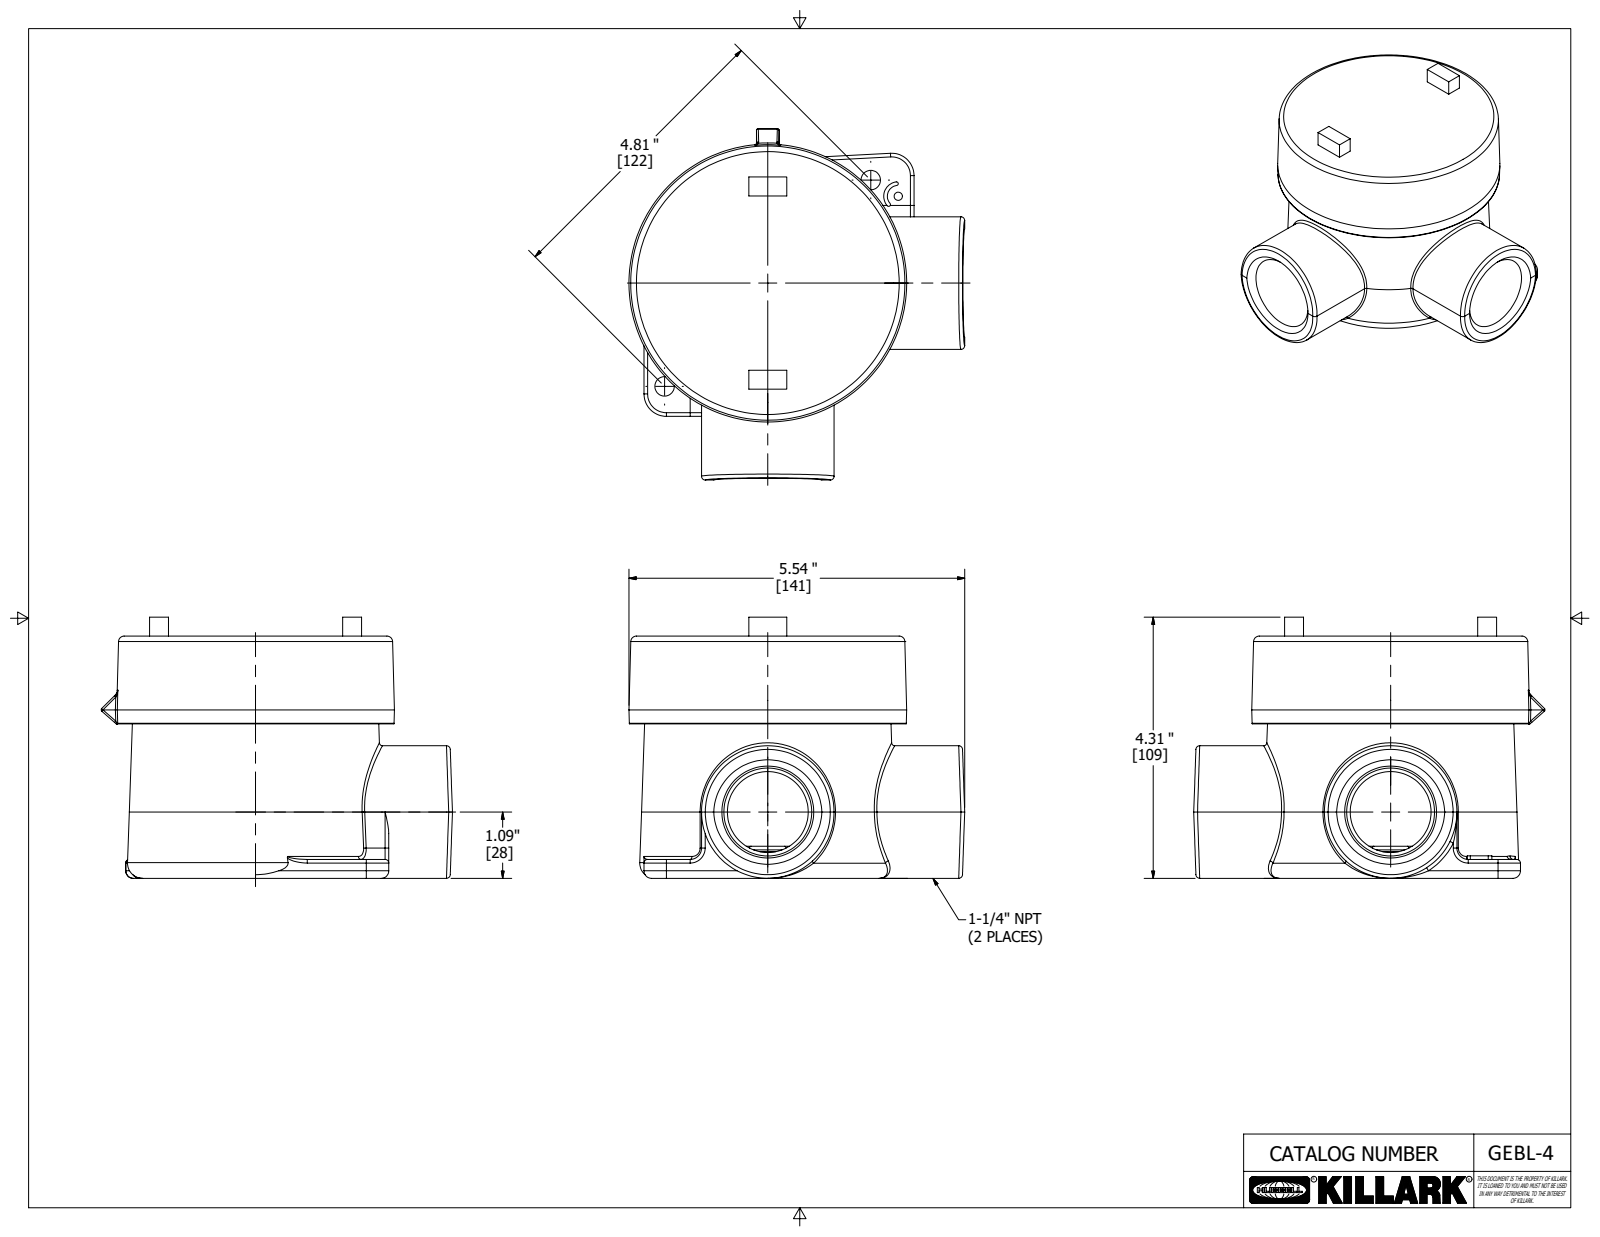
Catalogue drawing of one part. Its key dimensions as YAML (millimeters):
part_name: "GEBL-4; 21173; 21147-override"
step_written_by: "Autodesk Inventor 2020 (AUTOMOTIVE_DESIGN)"
units: millimeters
bodies: {solids: 2, faces: 809, planar: 414, cylindrical: 83, other: 312}
overall_size: [147.3, 140.8, 109.5]
volume: 575700
surface_area: 129400
round_holes:
  - {diameter: 8.2, count: 2}
  - {diameter: 33.9, count: 2}
  - {diameter: 39.6, count: 2}
  - {diameter: 3.5, count: 1}
  - {diameter: 97.1, count: 1}
  - {diameter: 102.7, count: 1}
round_bosses_or_shafts:
  - {diameter: 55.6, count: 2}
partial_cylinders:
  - {radius: 1.5, count: 33}
  - {radius: 0.8, count: 12}
  - {radius: 3.2, count: 4}
  - {radius: 0.8, count: 3}
  - {radius: 4.7, count: 2}
  - {radius: 9.4, count: 2}
  - {radius: 4.6, count: 1}
  - {radius: 6.1, count: 1}
face_to_face_distances: [101.5, 90.4, 11.1, 64.7, 25.7, 36.8, 88.9, 9.7, 55.1, 80.8]
hole_center_spacings: [13.4, 61, 61.2, 65.7, 122.3, 126.3]
